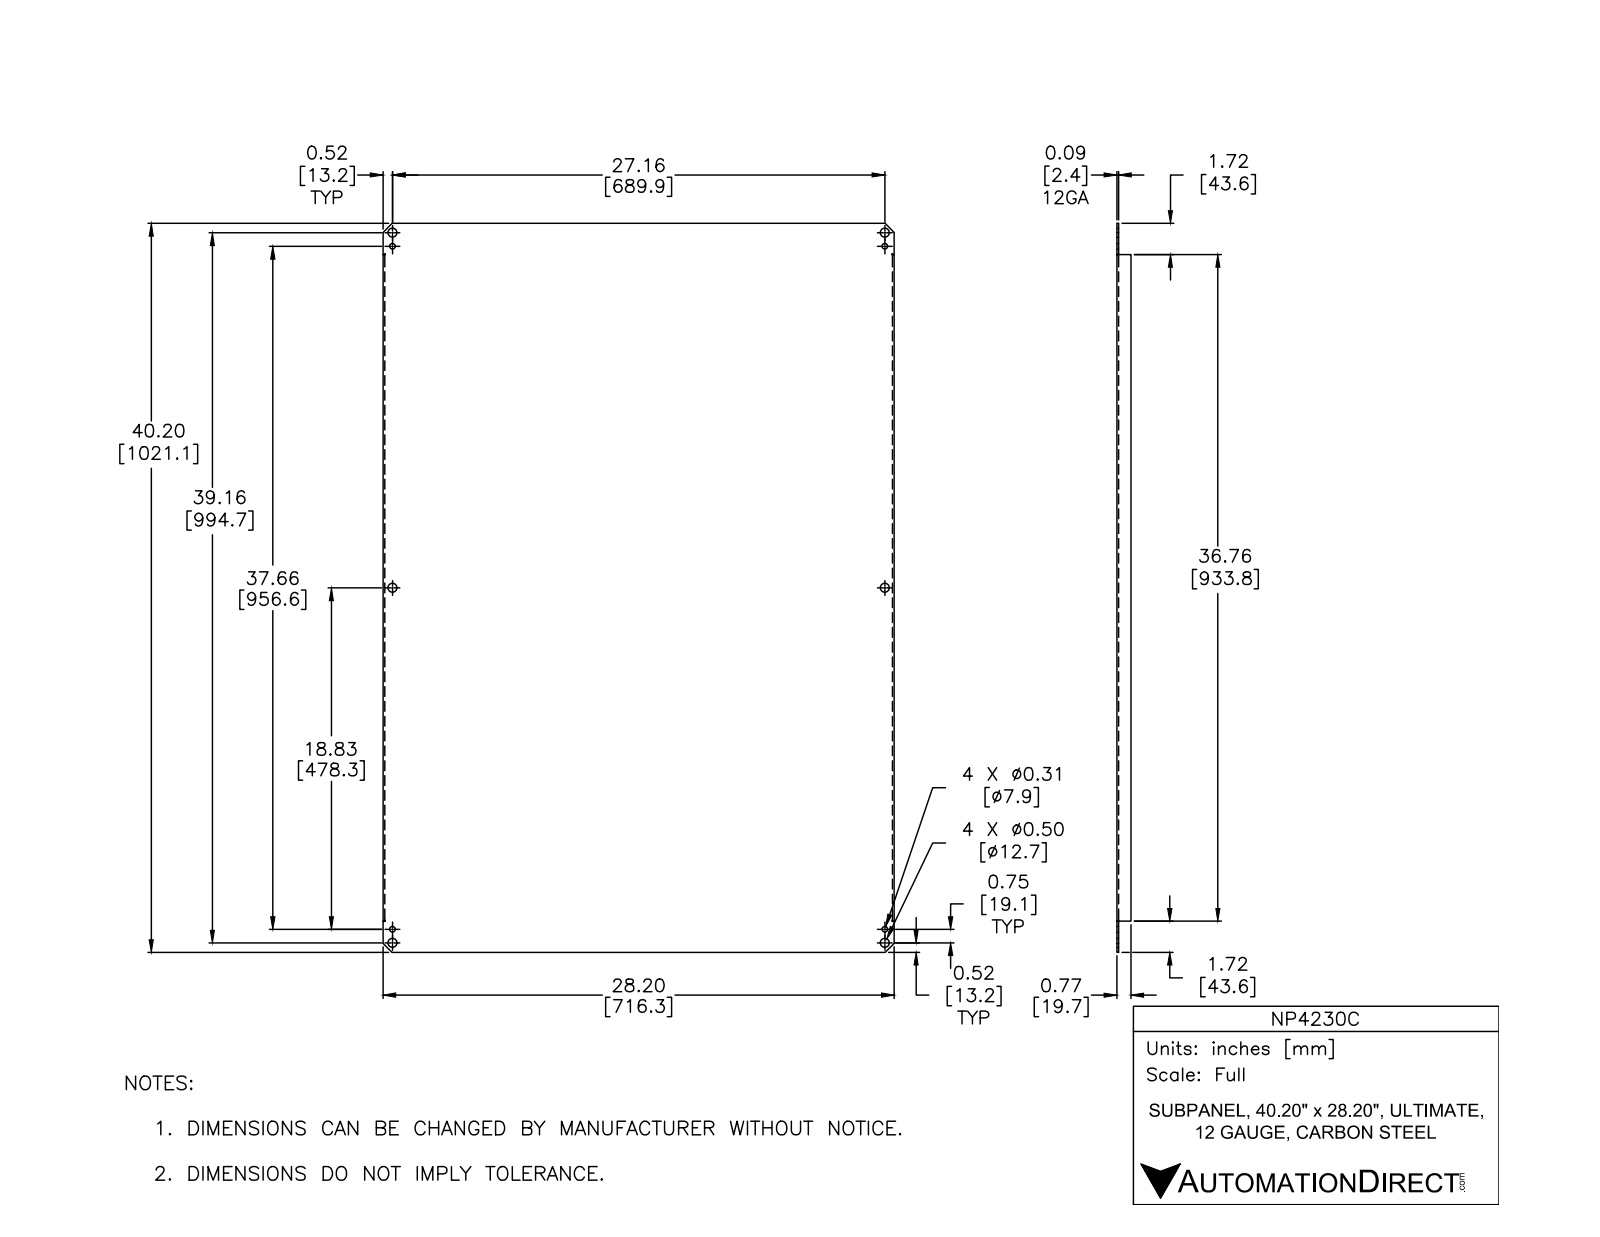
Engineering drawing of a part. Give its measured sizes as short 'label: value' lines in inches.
name: NP4230C
written by: Autodesk Inventor 2012 (AUTOMOTIVE_DESIGN)
unit: in
bodies: 1 solid, 68 faces (50 planar, 18 cylindrical, 0 other)
size: 40.2 × 28.2 × 0.774
volume: 113.6 in³; area: 2 439 in²
holes: 6× ⌀0.5, 4× ⌀0.313
rounds: 4× R0.016, 4× R0.109
face distances: 0.094, 28.106, 40.106, 28.2, 28.013, 40.2, 40.013, 0.68, 0.774, 1.718
hole spacings: 27.16, 0.75, 18.83, 19.58, 27.17, 33.049, 33.482, 38.41
